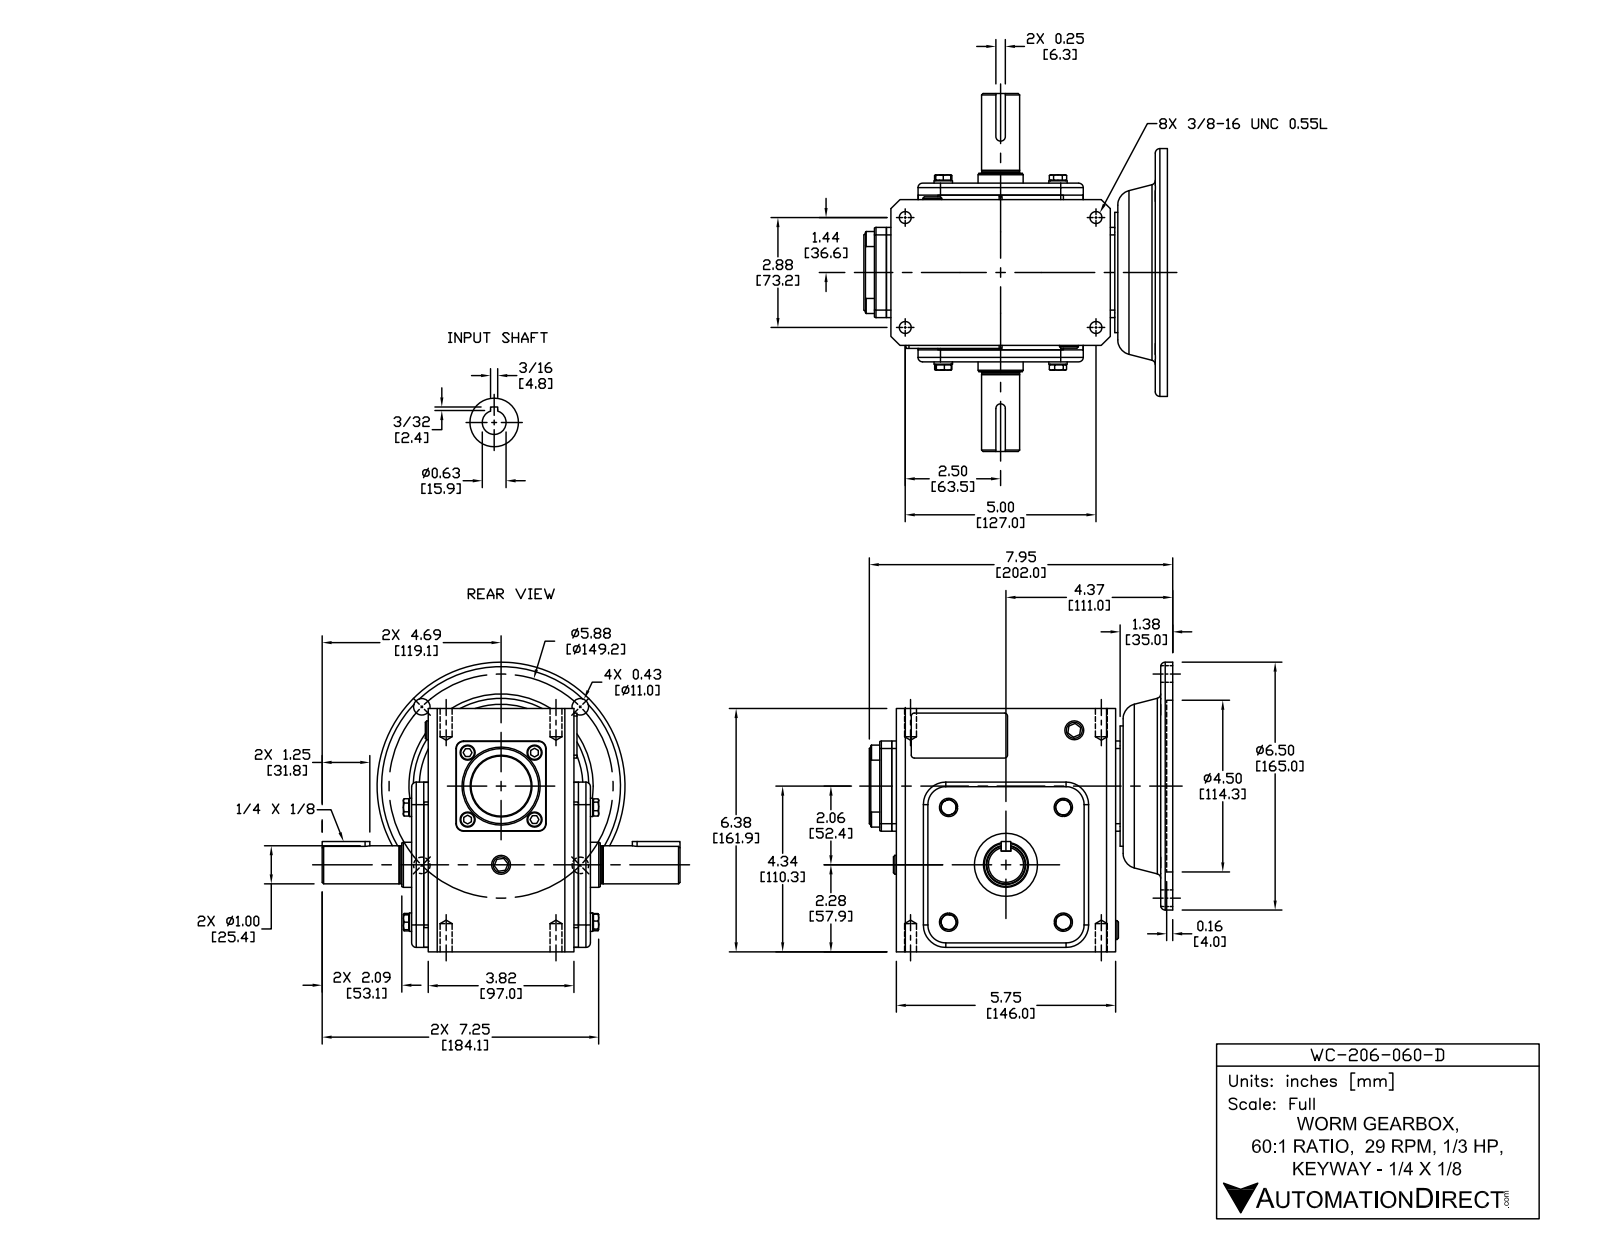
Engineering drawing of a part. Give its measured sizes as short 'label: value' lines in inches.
name: WG-206-060-D
written by: SolidWorks 2015 (CONFIG_CONTROL_DESIGN)
unit: in
bodies: 45 solids, 639 faces (311 planar, 194 cylindrical, 134 other)
size: 9.38 × 7.953 × 7.591
volume: 174.7 in³; area: 422.9 in²
holes: 4× ⌀0.313, 4× ⌀0.406, 1× ⌀0.591, 1× ⌀0.625, 1× ⌀1.181, 1× ⌀1.457, 1× ⌀1.654, 1× ⌀3.543, 1× ⌀4.5
bosses: 8× ⌀0.394, 4× ⌀0.48, 1× ⌀6.496, 1× ⌀3.15, 1× ⌀2.047, 1× ⌀1.575, 1× ⌀1.181, 1× ⌀1.142
rounds: 8× R0.079, 8× R0.118, 4× R0.197, 4× R0.591, 2× R0.02, 2× R0.039, 2× R0.125, 1× R2.717
face distances: 0.315, 0.118, 4.055, 0.433, 4.37, 4.252, 3.937, 6.375, 4.685, 0.709
hole spacings: 2.937, 4.154, 2.077, 2.88, 4.631, 5, 5.77, 5.875
